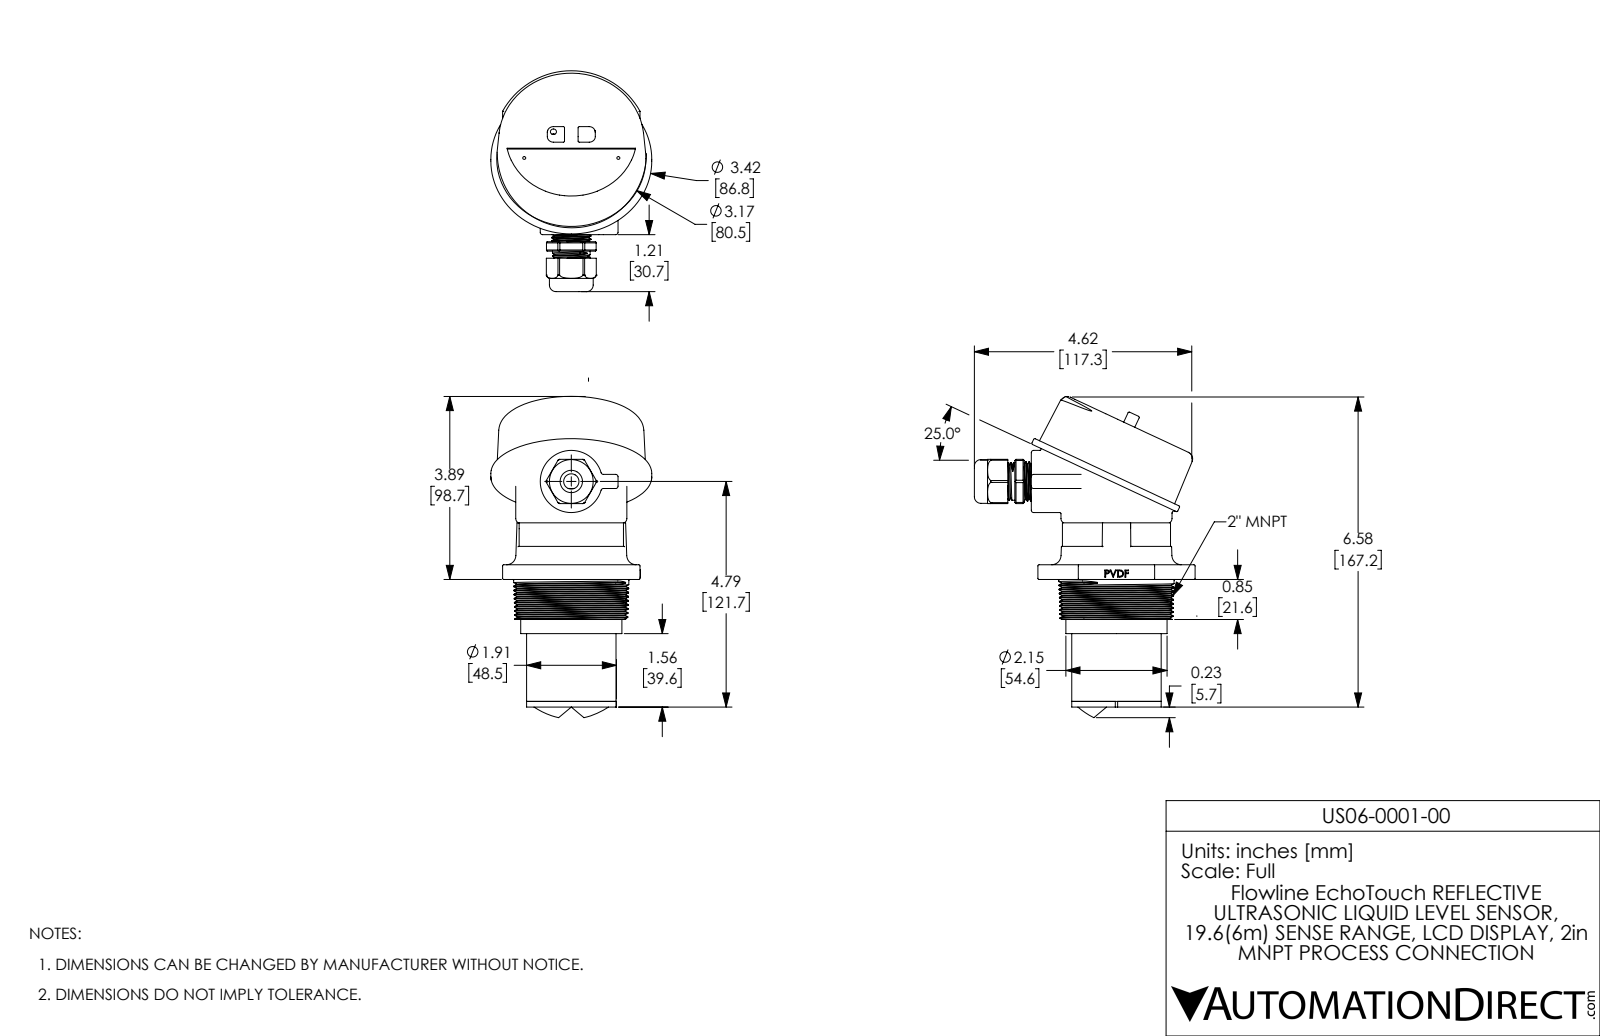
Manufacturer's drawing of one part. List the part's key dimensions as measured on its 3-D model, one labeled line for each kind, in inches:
Part name (STEP PRODUCT): US06-001-00
STEP written by: SolidWorks 2017 (AUTOMOTIVE_DESIGN)
Units: inches
Bodies: 7 solids, 526 faces (183 planar, 132 cylindrical, 211 other)
Overall size (bounding box): 6.824 × 4.69 × 3.419
Volume: 15.26 in³ · Surface area: 215.8 in²
Round holes (diameter × count): ⌀0.13 ×5, ⌀0.065 ×2, ⌀0.325 ×1, ⌀0.475 ×1, ⌀0.5 ×1, ⌀0.52 ×1, ⌀0.74 ×1, ⌀0.935 ×1, ⌀1.36 ×1, ⌀1.75 ×1, ⌀2.047 ×1, ⌀2.72 ×1
Round bosses / shafts (diameter × count): ⌀3.419 ×1, ⌀2.98 ×1, ⌀2.77 ×1, ⌀2.36 ×1, ⌀2.296 ×1, ⌀2.15 ×1, ⌀1.9 ×1, ⌀1.7 ×1
Partial cylindrical surfaces — rounded edges, fillets, slot ends (radius × count): R0.025 ×13, R0.05 ×7, R0.13 ×2, R0.82 ×1, R1.392 ×1, R1.67 ×1
Main face-to-face distances: 0.125, 0.05, 0.512, 0.462, 0.165, 0.2, 1.085, 1.25, 0.262, 0.312
Hole centre spacings: 1.021, 0.65, 0.787, 1.11, 0.38, 0.785, 1.299, 1.461
